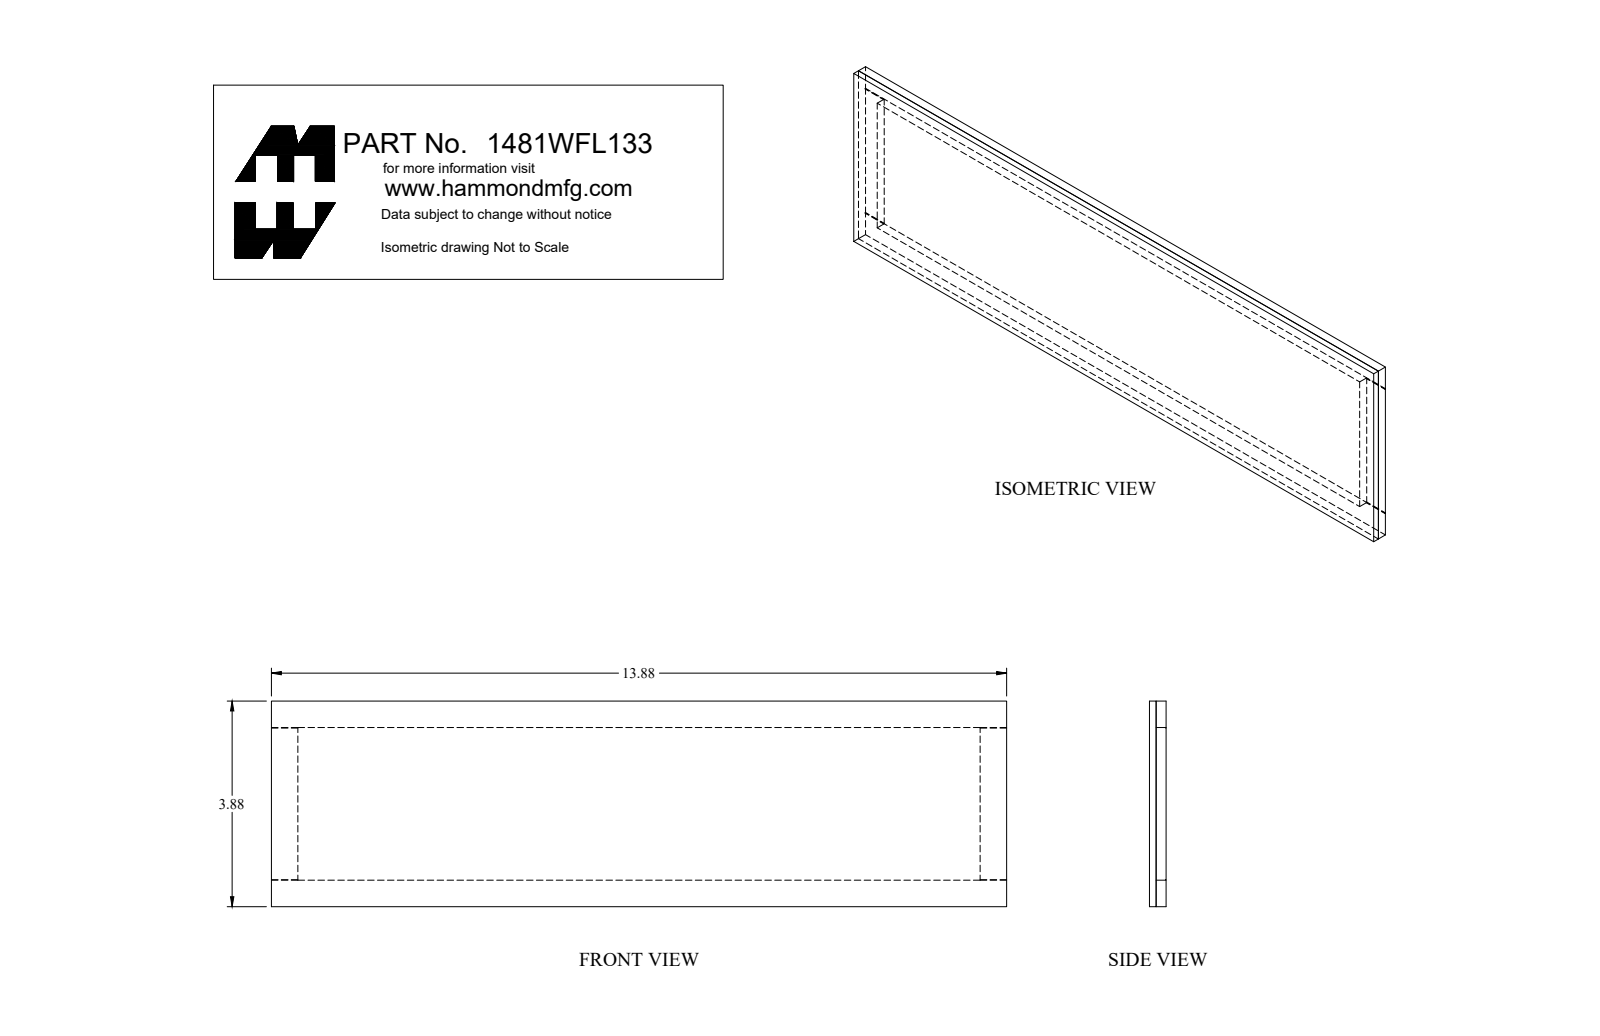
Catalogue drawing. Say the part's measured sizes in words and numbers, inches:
The part is named "1481WFL133_Default". Its 3-D file was written by "SolidWorks 2019 (CONFIG_CONTROL_DESIGN)". It is 2 solids with 27 faces: 27 planar, 0 cylindrical and 0 other. Overall it measures 13.88 by 3.88 by 0.313 inches. Its volume is 9.874 cubic inches and its surface area 158.3 square inches. The main face-to-face distances are 0.125, 0.313, 0.187, 0.5, 3.38, 3.88, 2.88, 13.88, 13.38, 12.88.
